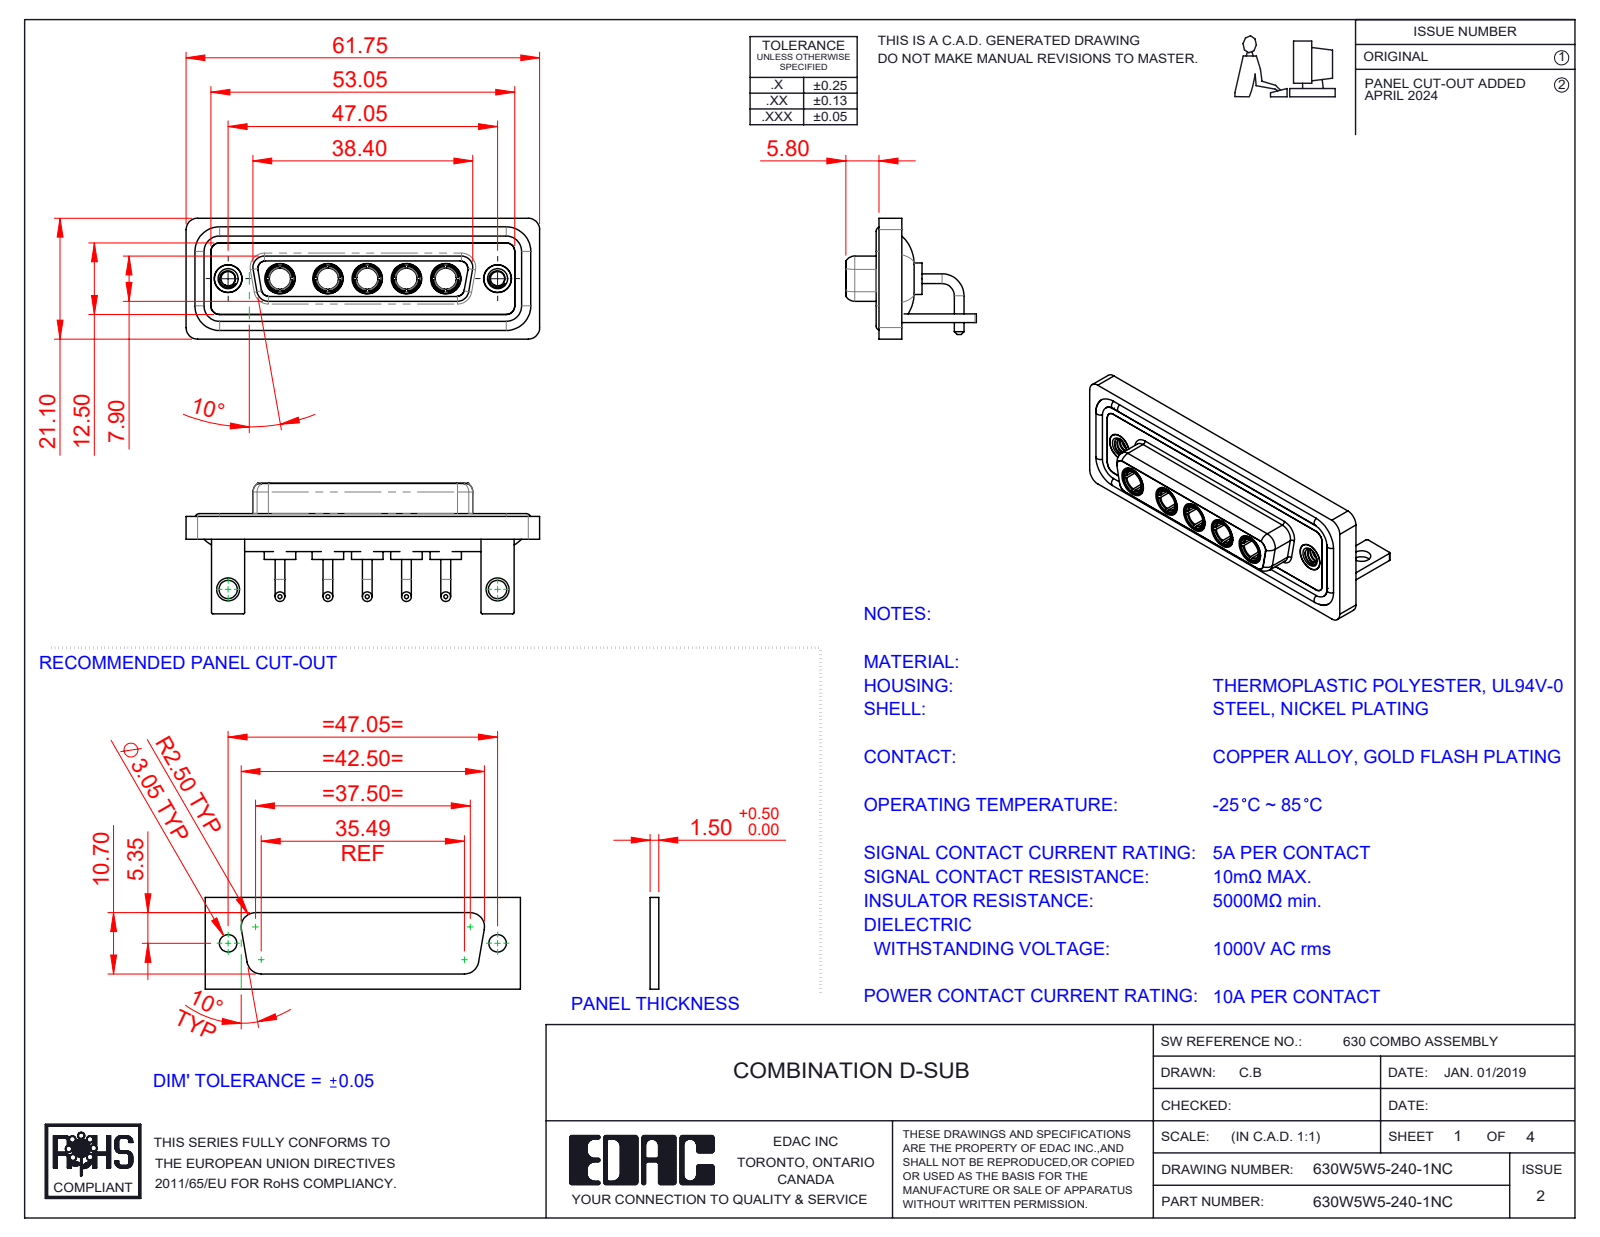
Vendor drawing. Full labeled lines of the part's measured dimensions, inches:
Part name (STEP PRODUCT): 630Combo Waterproof Housing_25 Contacts; 630Combo Stabilizer Bracket_50 Contacts; 630Combo Shell Front_25 Contacts; 630Combo Shell Rear_25 Contacts (+4 more)
STEP written by: SolidWorks 2023 (CONFIG_CONTROL_DESIGN)
Units: inches
Bodies: 19 solids, 818 faces (270 planar, 335 cylindrical, 213 other)
Overall size (bounding box): 2.431 × 0.898 × 0.831
Volume: 0.519 in³ · Surface area: 22.16 in²
Round holes (diameter × count): ⌀0.191 ×7, ⌀0.146 ×5, ⌀0.209 ×5, ⌀0.098 ×2, ⌀0.126 ×2, ⌀0.157 ×2, ⌀0.159 ×2, ⌀0.197 ×2
Round bosses / shafts (diameter × count): ⌀0.067 ×10, ⌀0.217 ×5, ⌀0.205 ×5, ⌀0.195 ×5, ⌀0.187 ×5, ⌀0.148 ×5, ⌀0.063 ×4, ⌀0.195 ×2
Partial cylindrical surfaces — rounded edges, fillets, slot ends (radius × count): R0.079 ×19, R0.059 ×18, R0.01 ×16, R0.053 ×8, R0.063 ×8, R0.02 ×5, R0.083 ×5, R0.024 ×4
Main face-to-face distances: 0.016, 0.071, 0.059, 0.114, 0.146, 0.161, 0.043, 0.055, 0.063, 0.098
Hole centre spacings: 0.27, 0.356, 1.496, 1.852, 0.27, 0.33, 0.54, 0.541
